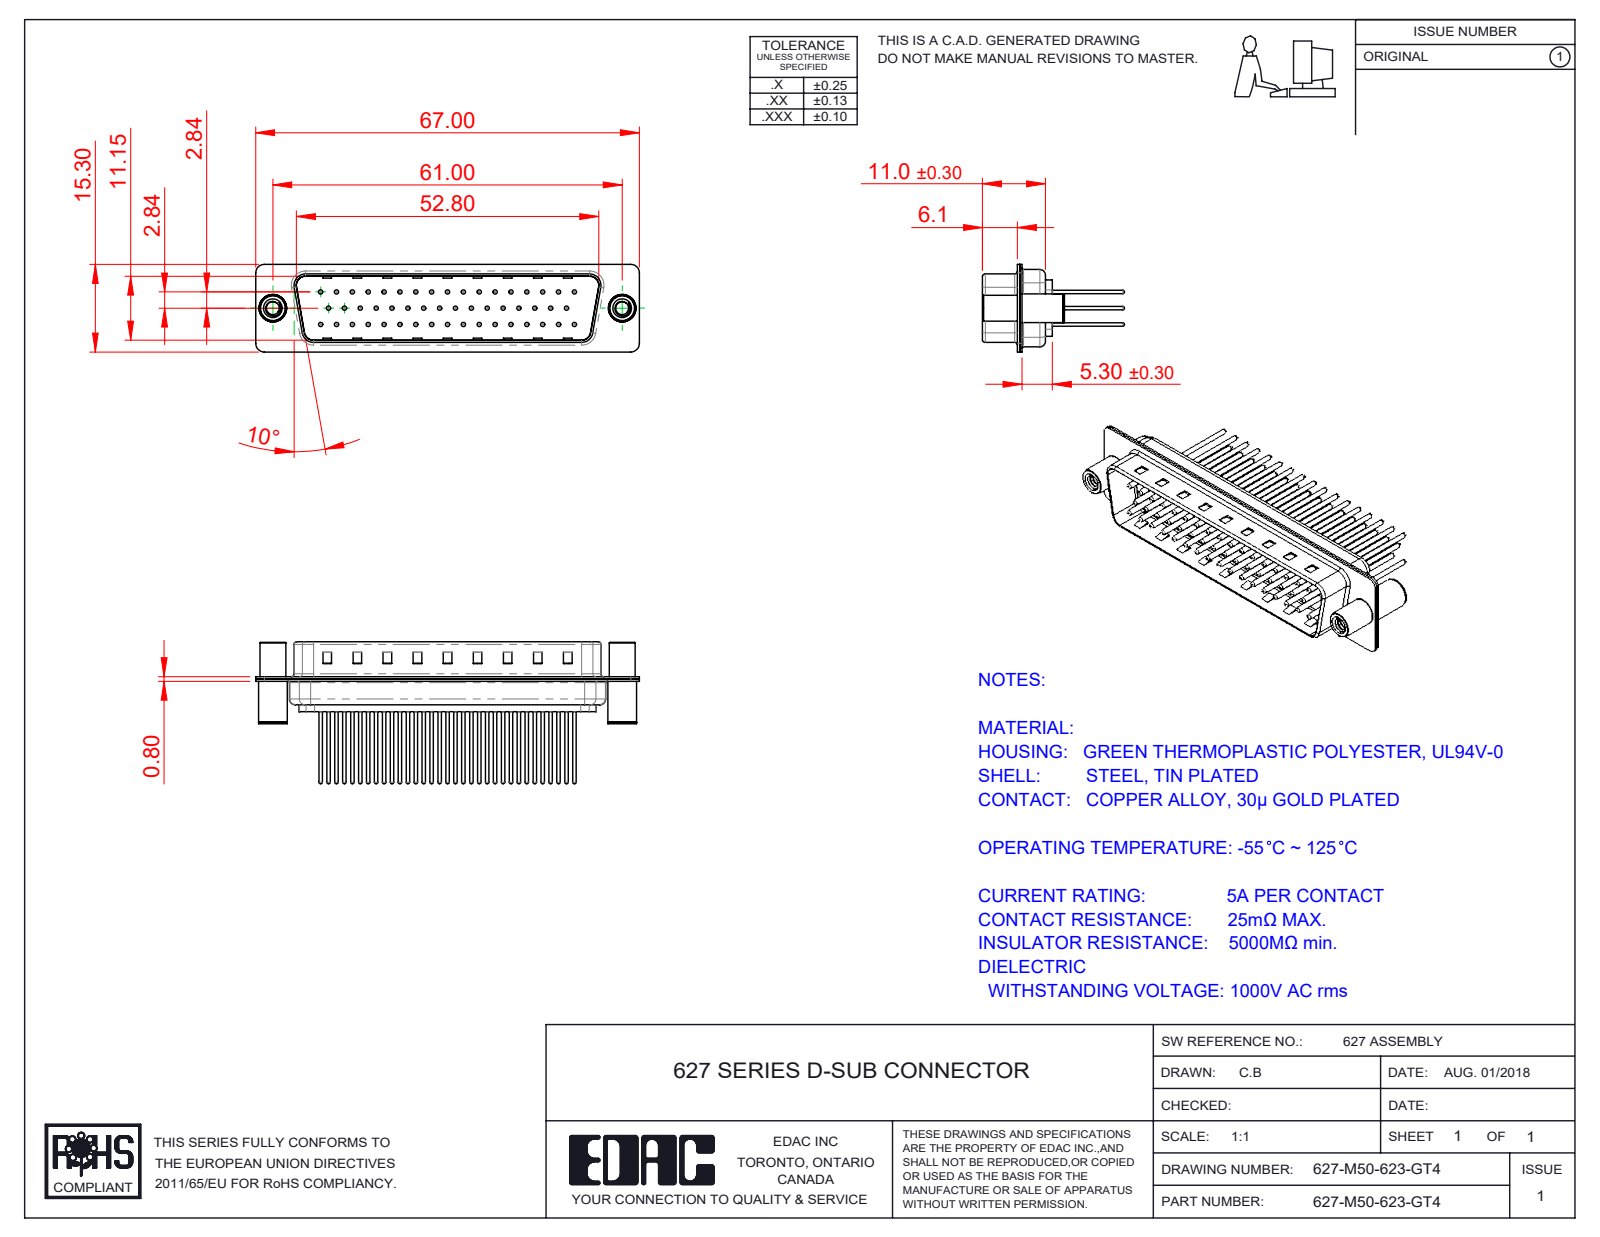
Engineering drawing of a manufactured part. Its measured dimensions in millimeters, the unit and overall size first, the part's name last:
Units: millimetres
Overall size (bounding box): 67 × 24.77 × 15.3
Round holes (diameter × count): ⌀0.75 ×50, ⌀1.6 ×50, ⌀2 ×50, ⌀2.26 ×2, ⌀3.26 ×2, ⌀4 ×2, ⌀4.8 ×2
Round bosses / shafts (diameter × count): ⌀1.5 ×50, ⌀0.6 ×50, ⌀5 ×2, ⌀4.9 ×2, ⌀4.5 ×2
Partial cylindrical surfaces — rounded edges, fillets, slot ends (radius × count): R1.5 ×16, R2 ×12, R0.5 ×8, R1.6 ×8, R0.25 ×4, R0.6 ×4, R0.65 ×4, R0.9 ×4
Main face-to-face distances: 0.4, 11.55, 5.7, 6.1, 0.78, 0.77, 12.33, 5.3, 12.32, 13.1
Hole centre spacings: 3.16, 2.77, 5.54, 8.31, 11.08, 13.85, 16.62, 5.03
Volume: 4 909 mm³ · Surface area: 11 876 mm²
Bodies: 55 solids, 2348 faces (559 planar, 893 cylindrical, 896 other)
Part name (STEP PRODUCT): 627M Shell Front_50 Contacts; 627-M50-623-GT4; 627M Housing_50 Contacts; 627M Contact Row 2_23 (+4 more)
STEP written by: SolidWorks 2020 (CONFIG_CONTROL_DESIGN)
